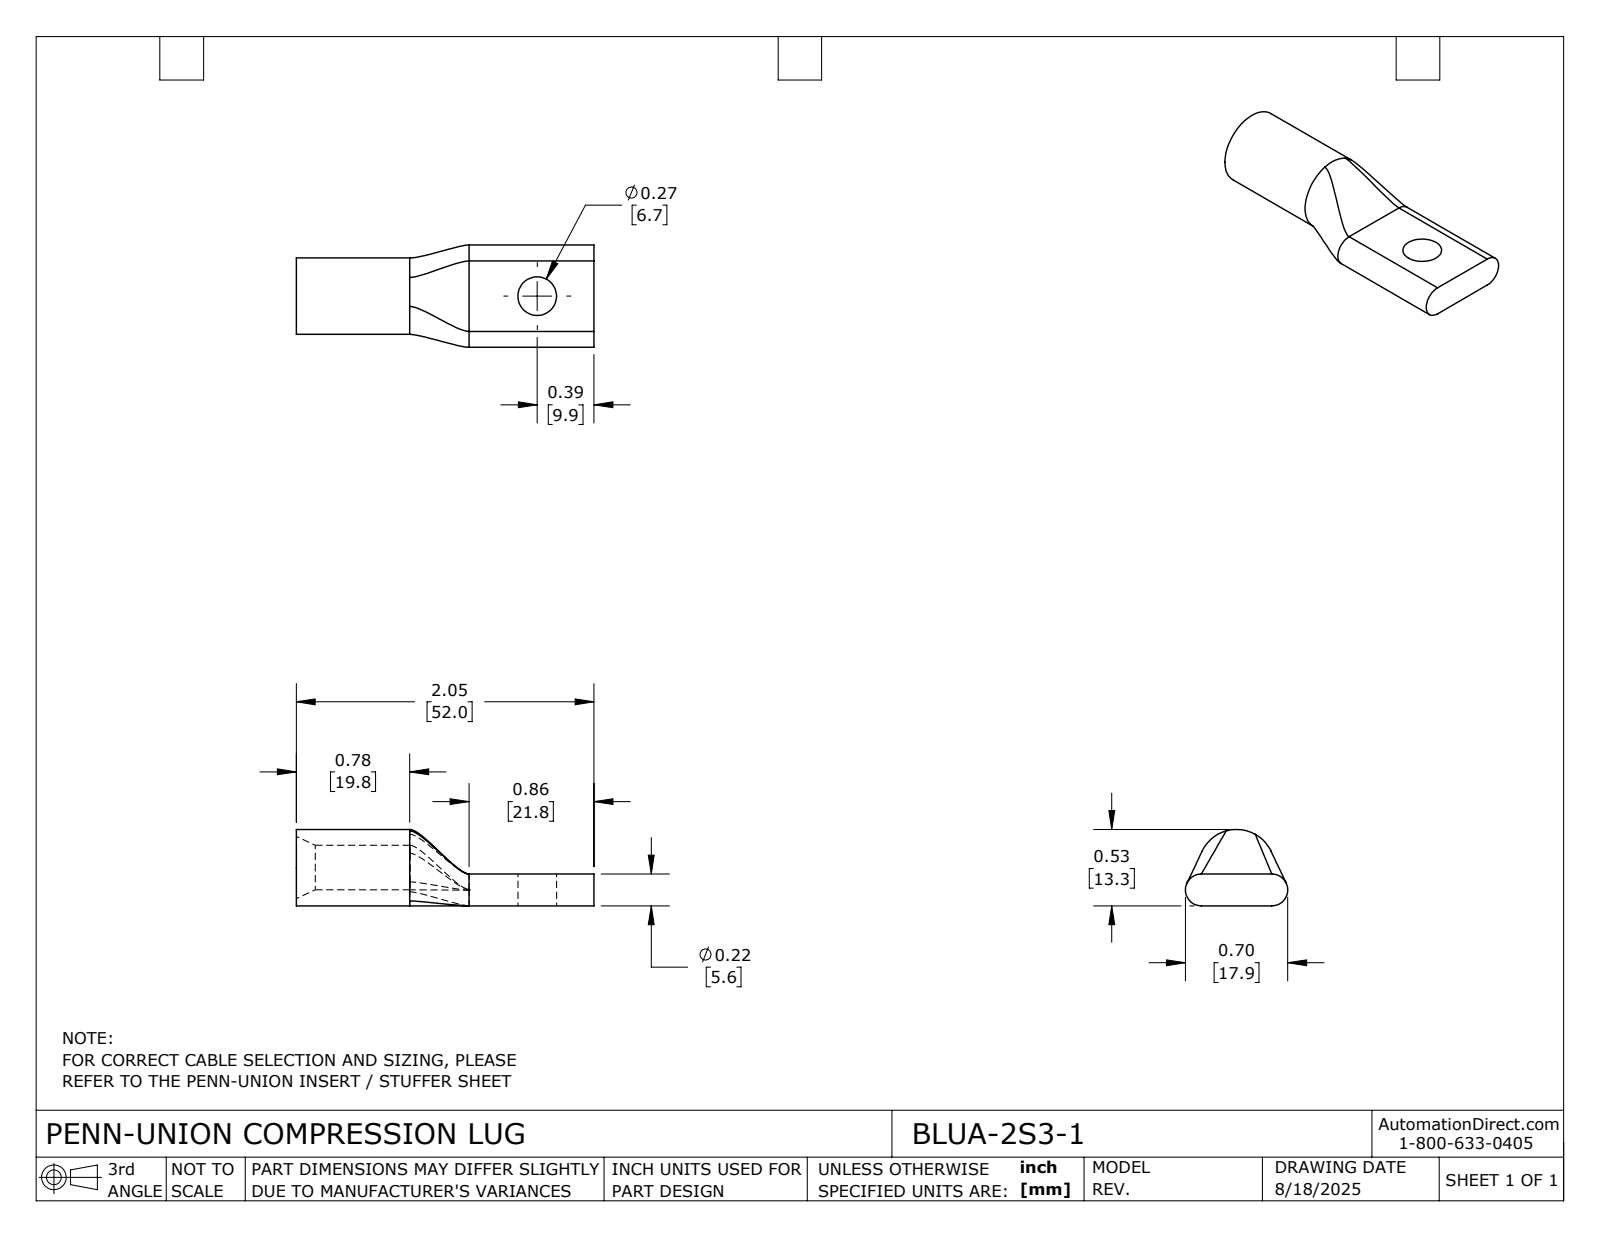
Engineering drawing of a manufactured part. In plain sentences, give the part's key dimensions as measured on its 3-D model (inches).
The part is named "BLUA-2S3-1". Its 3-D file was written by "SolidWorks 2024 (CONFIG_CONTROL_DESIGN)". It is 1 solid with 24 faces: 5 planar, 9 cylindrical and 10 other. Overall it measures 2.047 by 0.703 by 0.525 inches. Its volume is 0.276 cubic inches and its surface area 4.934 square inches. Round holes: 1 of diameter 0.266, 1 of diameter 0.306. Round bosses or shafts: 1 of diameter 0.525. Partial cylindrical surfaces (rounded edges, fillets, slot ends): 2 of radius 0.109. The main face-to-face distances are 0.219, 2.047, 1.187, 0.859.
